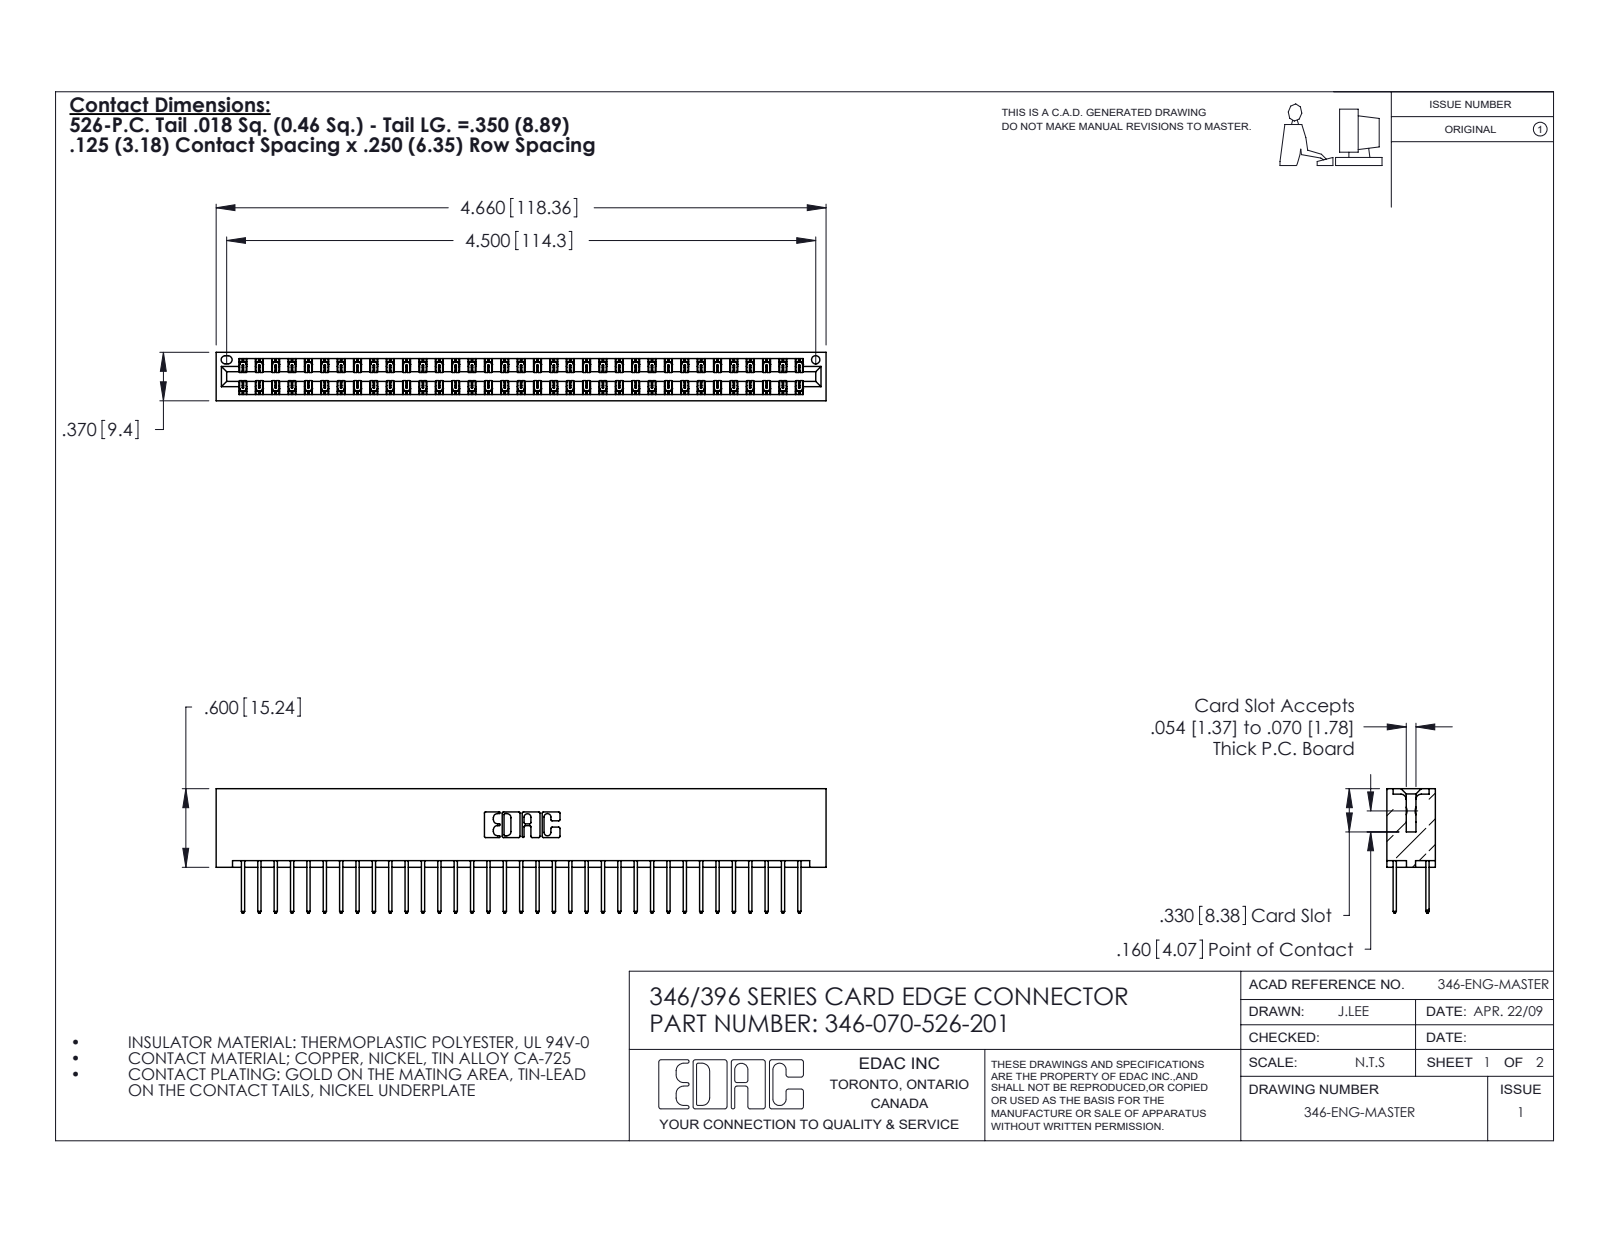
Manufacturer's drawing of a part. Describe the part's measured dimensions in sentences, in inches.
The part is named "346-070-526-201; 345-292-001_345-293-126; 346 Part_No Mounting Lugs". Its 3-D file was written by "SolidWorks 2020 (CONFIG_CONTROL_DESIGN)". It is 71 solids with 3754 faces: 2522 planar, 1232 cylindrical and 0 other. Overall it measures 4.66 by 0.95 by 0.37 inches. Its volume is 0.743 cubic inches and its surface area 26.82 square inches. Round holes: 1 of diameter 0.064. Partial cylindrical surfaces (rounded edges, fillets, slot ends): 105 of radius 0.006, 70 of radius 0.01, 22 of radius 0.01, 6 of radius 0.007, 6 of radius 0.031, 3 of radius 0.026, 2 of radius 0.014, 2 of radius 0.022. The main face-to-face distances are 0.048, 0.322, 0.25, 0.37, 0.072, 0.298, 0.025, 0.275, 0.148, 0.222.
